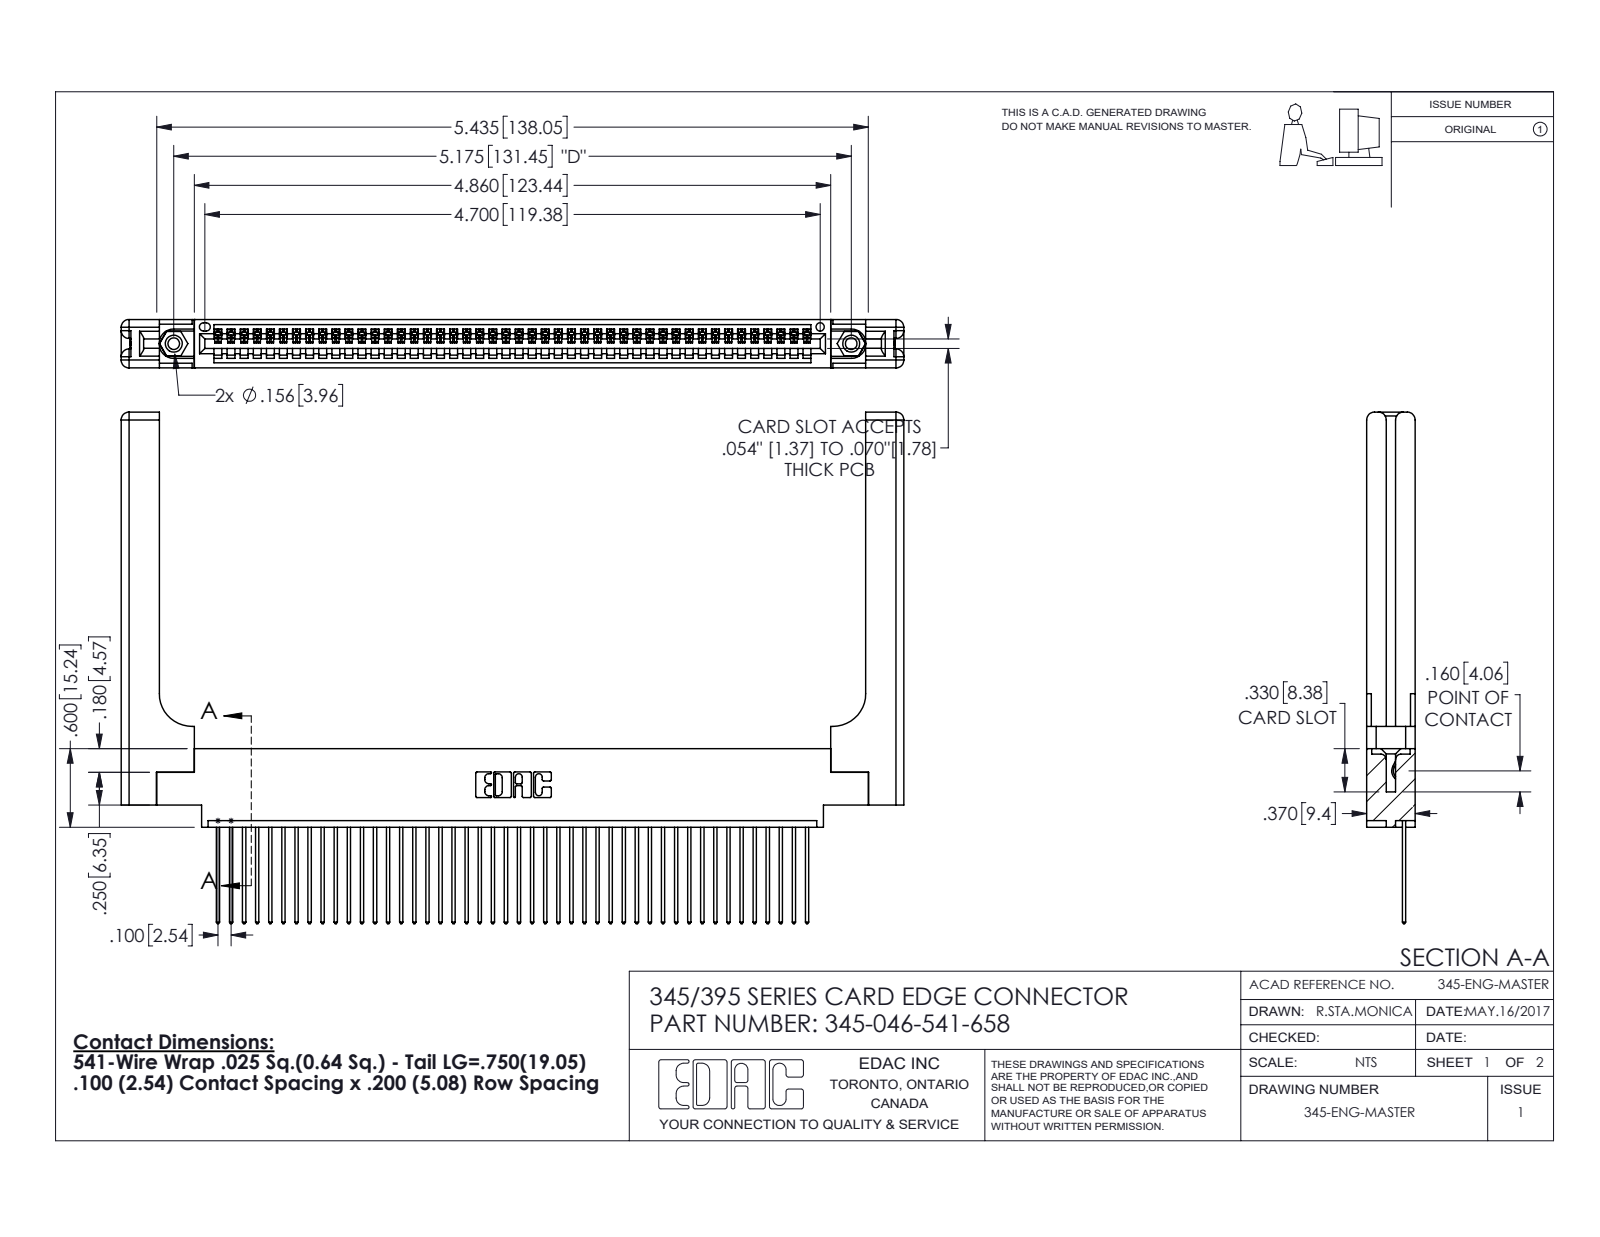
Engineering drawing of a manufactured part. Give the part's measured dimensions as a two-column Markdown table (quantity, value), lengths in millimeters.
| quantity | value |
| --- | --- |
| part name | 345-292-001_345-293-141; 345-046-541-658; 345-250-001_345-250-001-102; 345 Part_0.170 Offset - 0.156 Dia-TH (+1 more) |
| STEP written by | SolidWorks 2016 (CONFIG_CONTROL_DESIGN) |
| units | millimeters |
| bodies | 51 solids, 3054 faces (2072 planar, 922 cylindrical, 60 other) |
| overall size | 151.9 × 99.2 × 9.4 |
| volume | 23 010 mm³ |
| surface area | 25 650 mm² |
| round holes (diameter × count) | 2.3 × 2, 3.2 × 2, 4 × 2, 1.6 × 1 |
| round bosses / shafts (diameter × count) | 3.9 × 2 |
| partial cylindrical surfaces (radius × count) | 0.2 × 92, 0.3 × 92, 0.3 × 22, 1.5 × 16, 0.2 × 6, 0.8 × 6, 0.7 × 3, 0.8 × 2 |
| main face-to-face distances | 1.8, 9.4, 7.6, 2.5, 6.9, 0.6, 5.1, 5.7, 3.8, 3.8 |
| hole center spacings | 6.9, 125.5, 131.4 |
